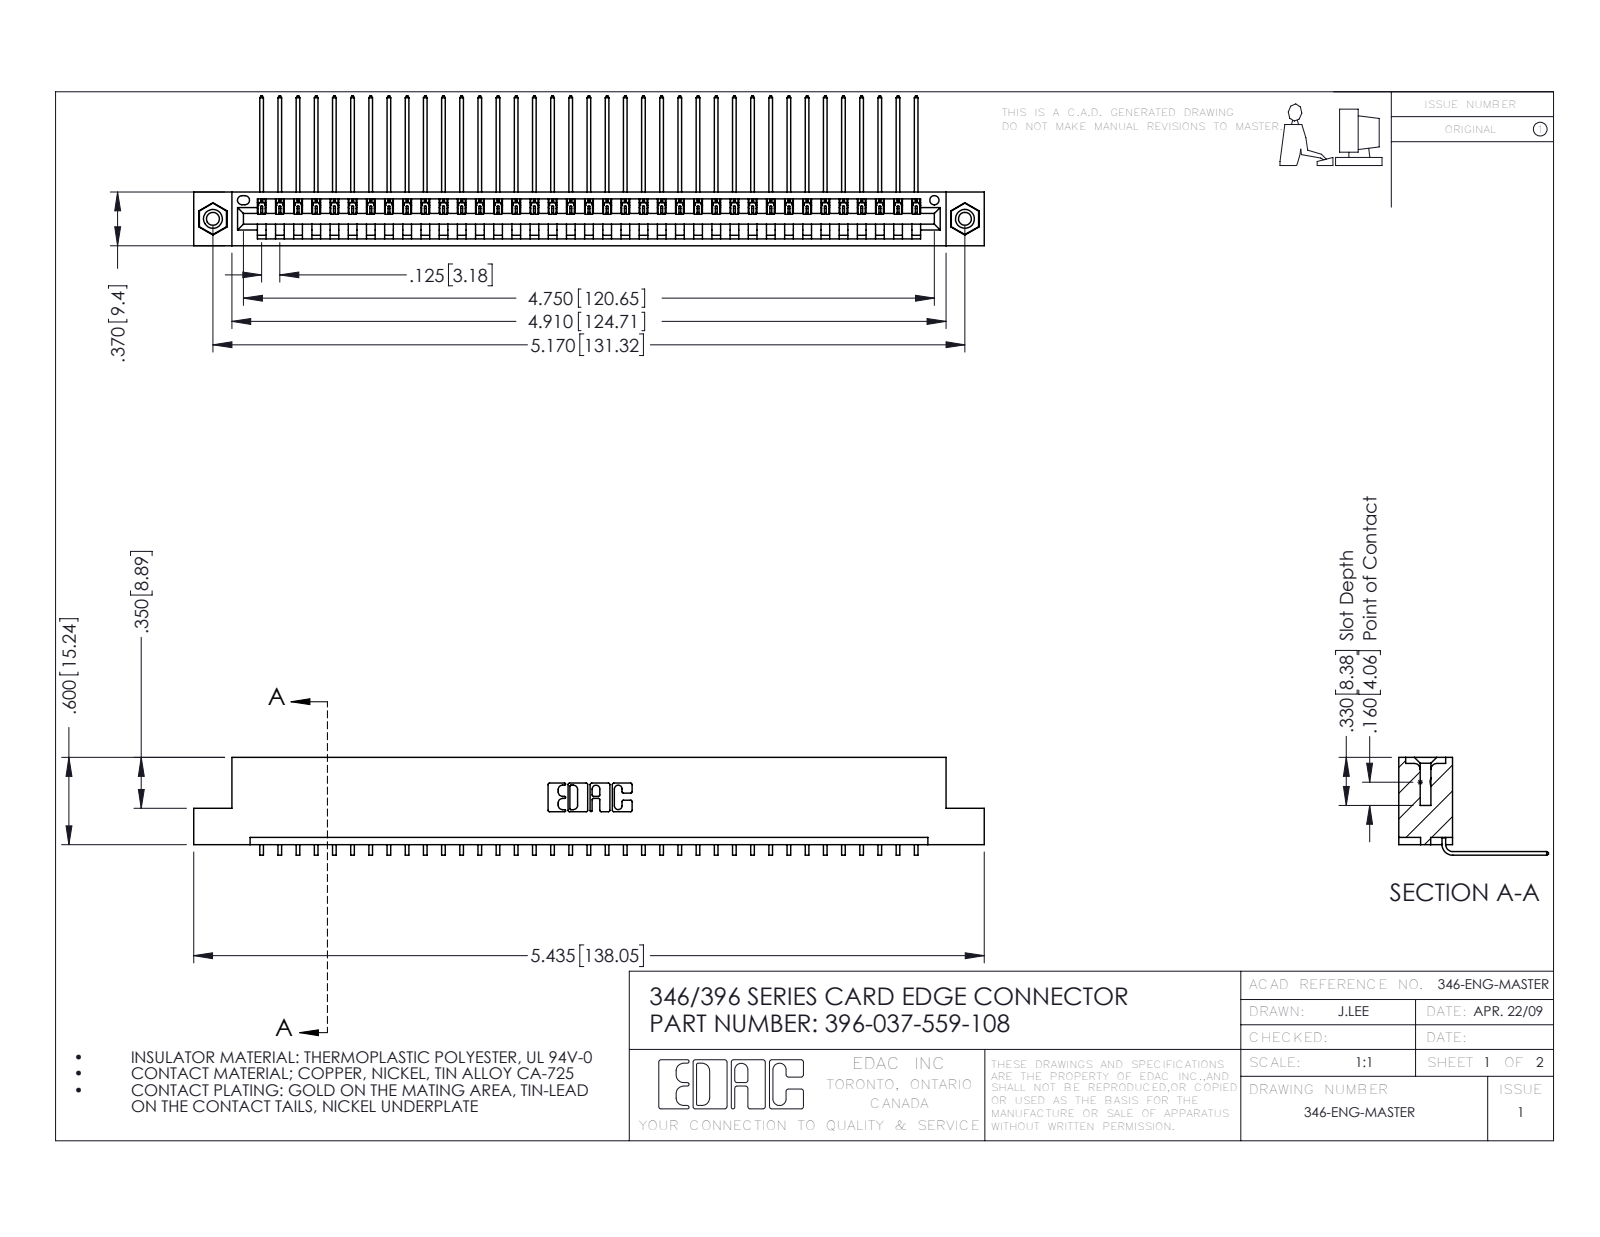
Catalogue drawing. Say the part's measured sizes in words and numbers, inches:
The part is named "396-037-559-108; 345-292-001_558 559 Tail - 1; 346 Part_Flush Mounting Lugs - 0.156 Dia-TI; 345-250-001_345-250-003-102". Its 3-D file was written by "SolidWorks 2016 (CONFIG_CONTROL_DESIGN)". It is 40 solids with 2402 faces: 1662 planar, 724 cylindrical and 16 other. Overall it measures 5.435 by 1.03 by 0.673 inches. Its volume is 0.811 cubic inches and its surface area 26.85 square inches. Round holes: 2 of diameter 0.089, 2 of diameter 0.125, 2 of diameter 0.156, 1 of diameter 0.064. Round bosses or shafts: 2 of diameter 0.155. Partial cylindrical surfaces (rounded edges, fillets, slot ends): 74 of radius 0.006, 22 of radius 0.01, 6 of radius 0.007, 6 of radius 0.031, 3 of radius 0.026, 2 of radius 0.031, 2 of radius 0.04, 1 of radius 0.014. The main face-to-face distances are 0.048, 0.322, 0.37, 0.25, 0.025, 0.072, 0.298, 0.148, 0.222, 0.1. The hole center spacings are 0.246, 4.961, 5.17.
